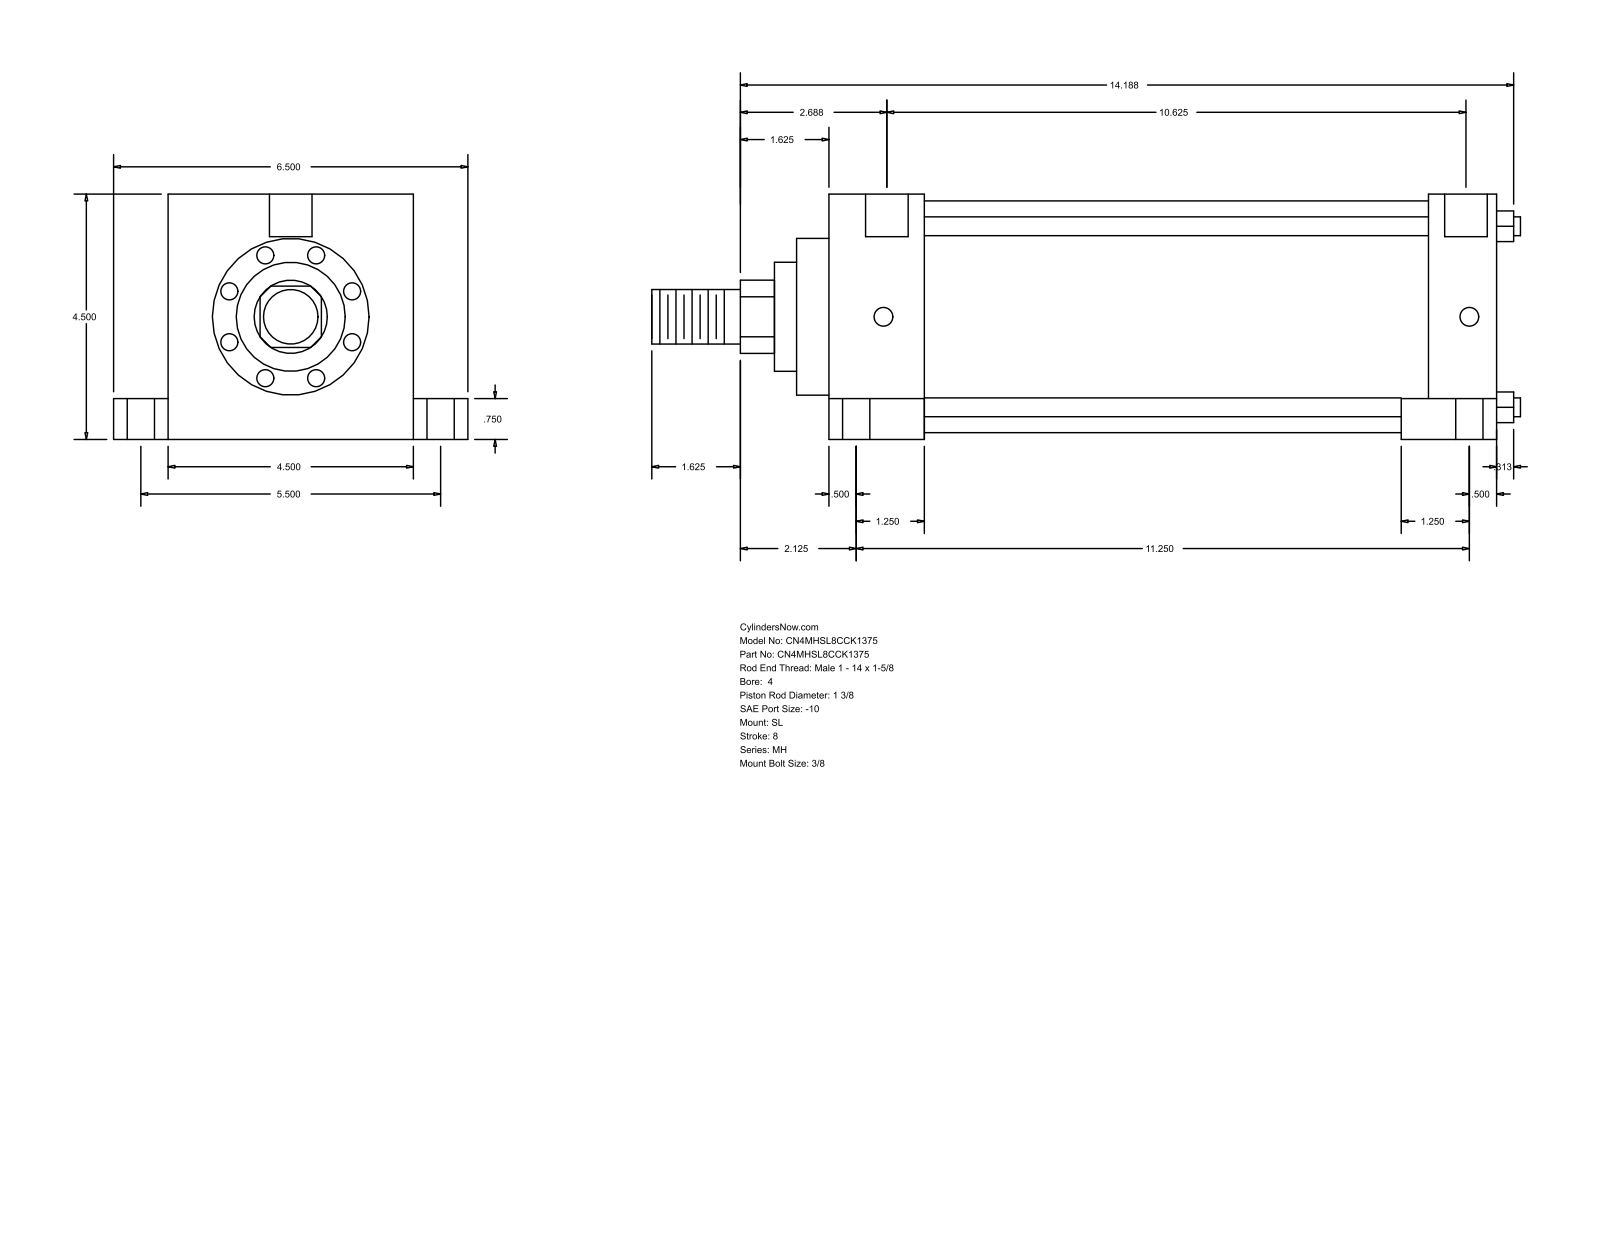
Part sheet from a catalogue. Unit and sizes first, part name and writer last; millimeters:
Units: millimetres
Overall size (bounding box): 404.81 × 165.1 × 114.3
Round holes (diameter × count): ⌀8.73 ×4, ⌀12.7 ×4, ⌀19.05 ×4, ⌀19.84 ×2
Round bosses / shafts (diameter × count): ⌀8.76 ×4, ⌀107.95 ×1, ⌀73.03 ×1, ⌀50.8 ×1, ⌀34.92 ×1, ⌀25.4 ×1
Partial cylindrical surfaces — rounded edges, fillets, slot ends (radius × count): R17.06 ×1
Main face-to-face distances: 114.3, 311.16, 44.45, 266.71, 279.41, 234.96, 31.75, 25.4, 139.7, 19.05
Hole centre spacings: 1.59, 69.85, 69.87, 70.99, 71.29, 139.7, 271.47, 273.06
Bodies: 0 solids, 110 faces (77 planar, 33 cylindrical, 0 other)
Part name (STEP PRODUCT): MH_SL__0400_1.375
STEP written by: GSSL Pune (CONFIG_CONTROL_DESIGN)
